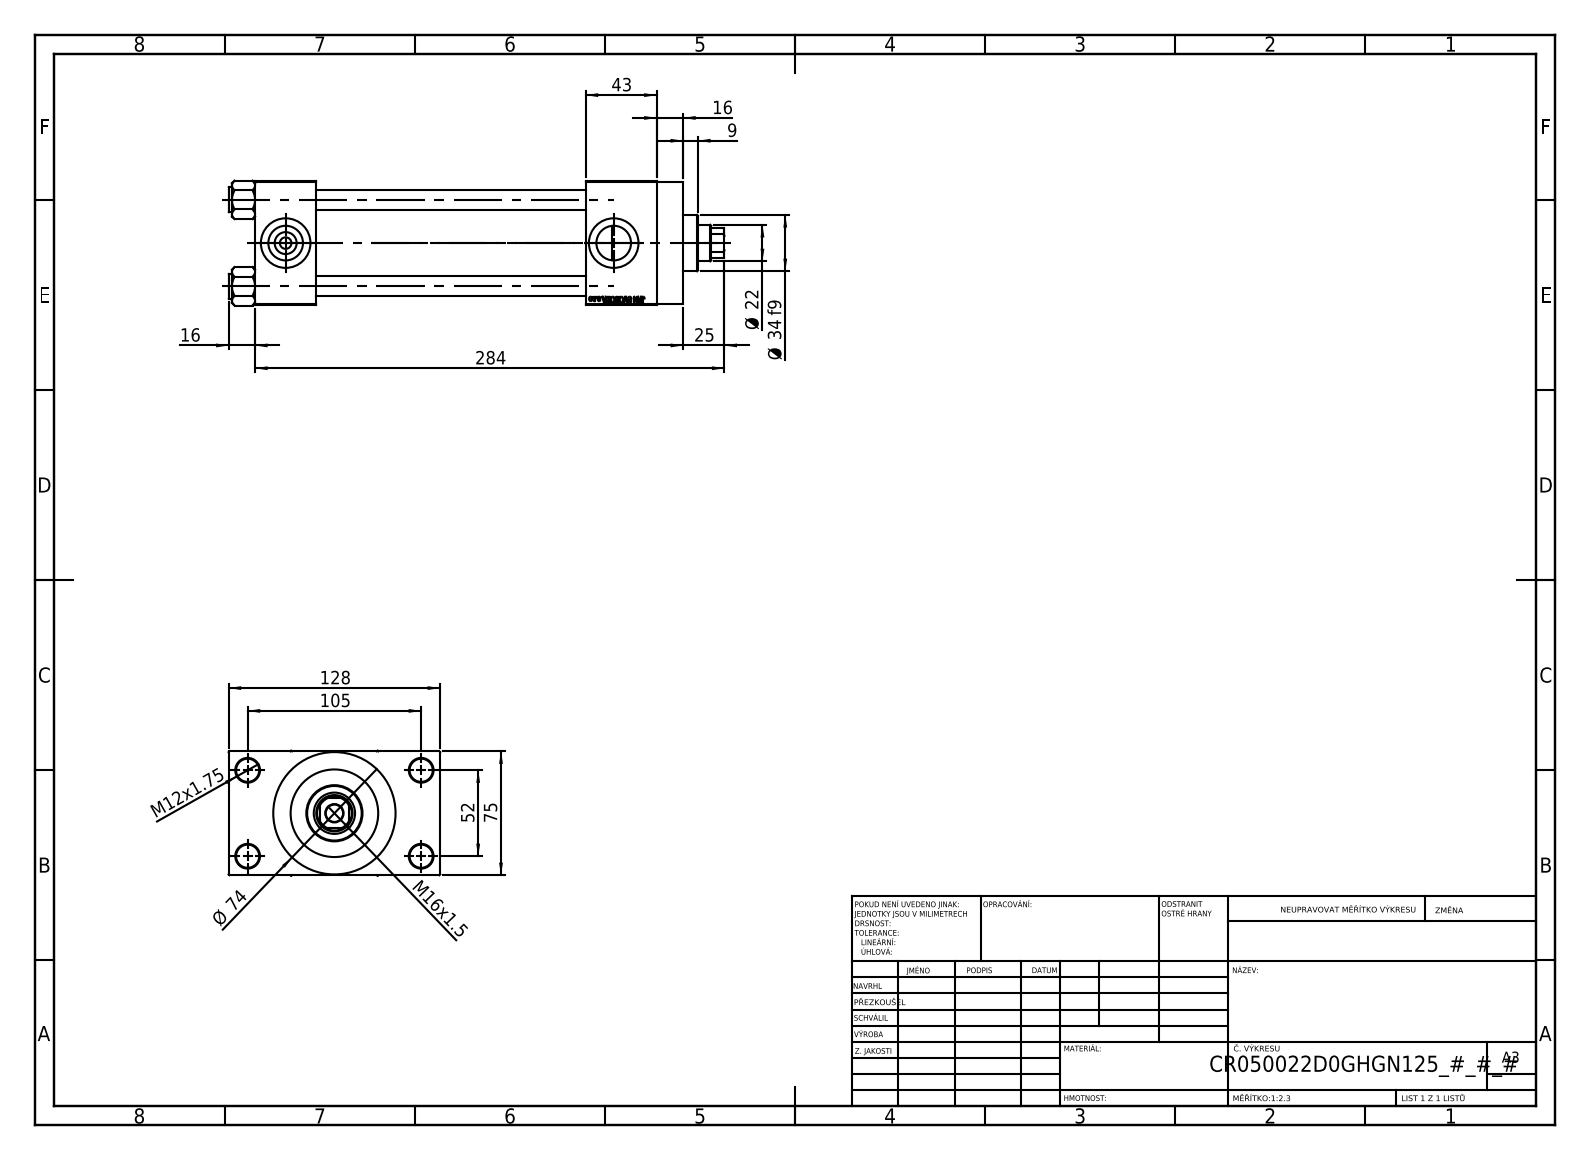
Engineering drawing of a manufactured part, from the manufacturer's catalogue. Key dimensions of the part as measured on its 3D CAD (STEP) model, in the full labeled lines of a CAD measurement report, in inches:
Part name (STEP PRODUCT): V215CR_D_Body; V215CR_VCP_D; NUT_M5_D; V215CR_D_TYCINKA (+1 more)
STEP written by: SolidWorks 2019 (CONFIG_CONTROL_DESIGN)
Units: inches
Bodies: 11 solids, 1103 faces (497 planar, 88 cylindrical, 518 other)
Overall size (bounding box): 11.811 × 5.039 × 2.974
Volume: 57.2 in³ · Surface area: 348.4 in²
Round holes (diameter × count): ⌀0.472 ×4, ⌀0.551 ×4, ⌀0.276 ×2, ⌀0.825 ×2, ⌀1.181 ×2, ⌀0.413 ×1, ⌀0.866 ×1, ⌀0.984 ×1, ⌀1.614 ×1, ⌀1.969 ×1, ⌀2.087 ×1
Round bosses / shafts (diameter × count): ⌀0.591 ×4, ⌀2.913 ×1, ⌀2.205 ×1, ⌀1.339 ×1
Partial cylindrical surfaces — rounded edges, fillets, slot ends (radius × count): R0.413 ×1
Main face-to-face distances: 2.953, 6.417, 1.457, 7.874, 1.043, 9.567, 8.11, 1.693, 3.996, 0.63
Hole centre spacings: 1.037, 1.456, 2.059, 2.3, 2.307, 3.096, 3.715, 2.047
